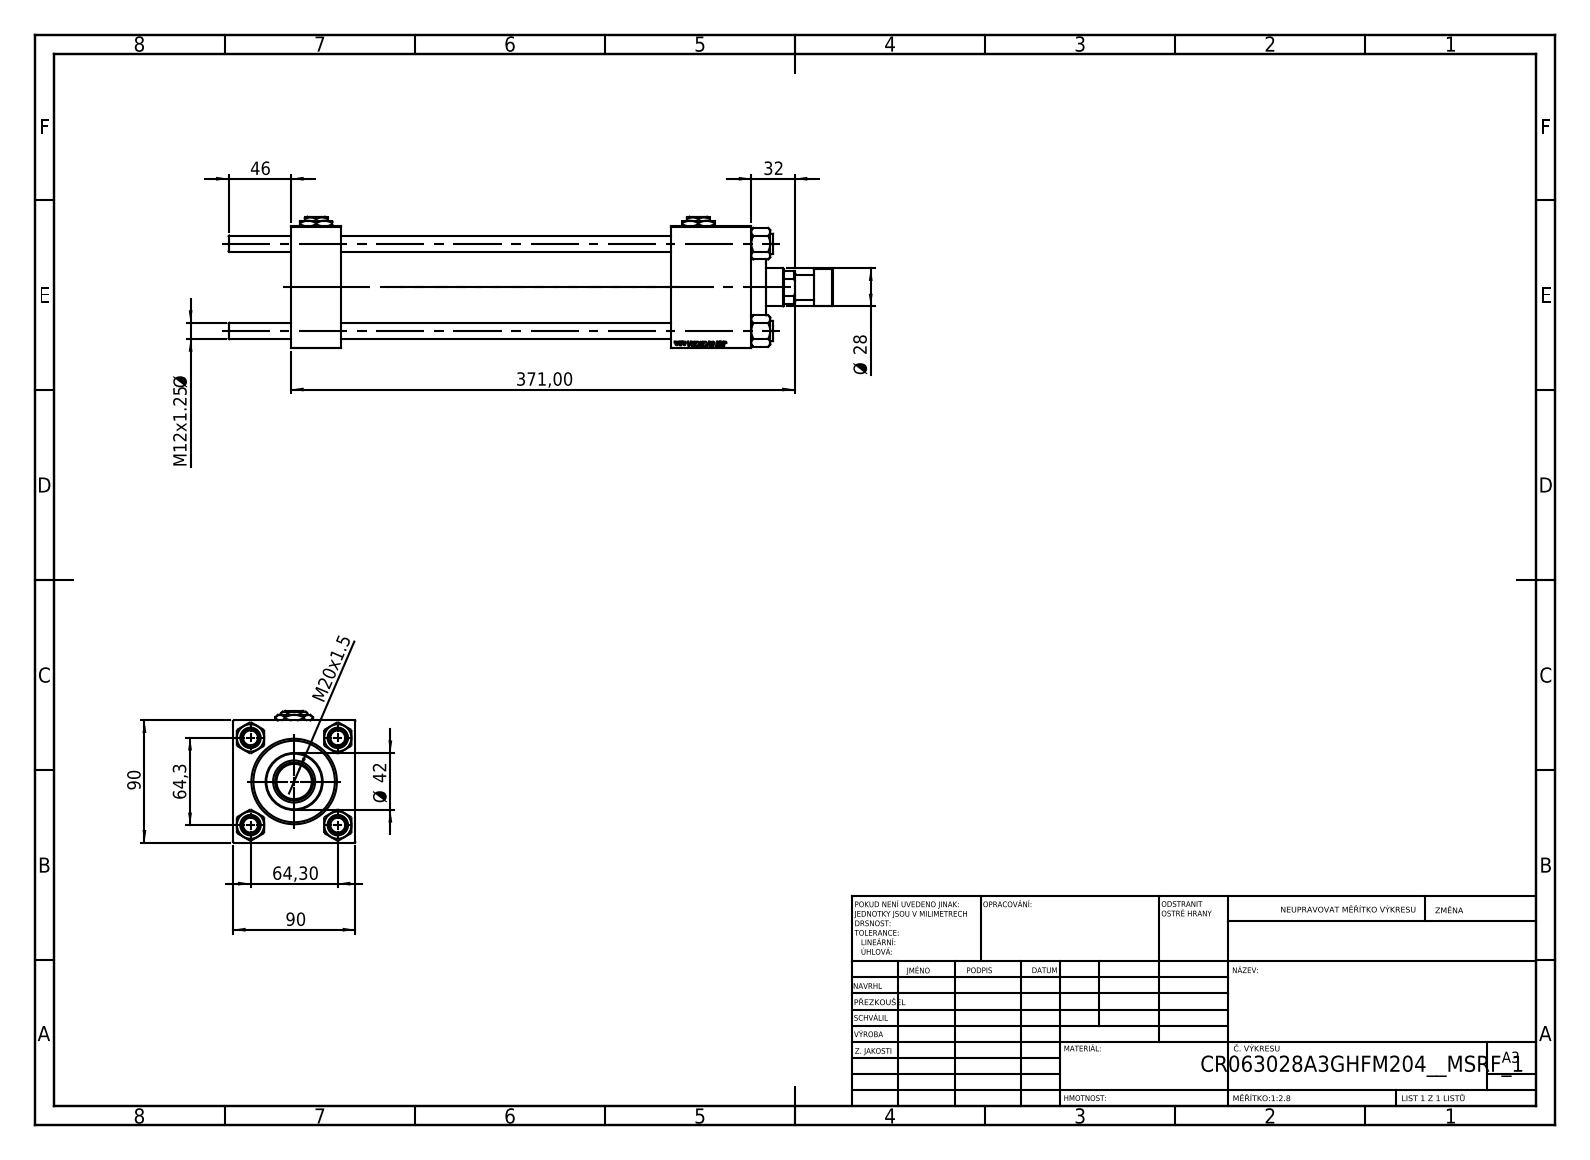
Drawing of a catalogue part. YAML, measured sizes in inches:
part_name: "V215_VC_A; CR025_012_A_0_G_A_G_M_020_+#_##_TYCINKA; NUT_M5; Zatka_pro_OIL_PORT (+3 more)"
step_written_by: "SolidWorks 2019 (CONFIG_CONTROL_DESIGN)"
units: inches
bodies: {solids: 14, faces: 1247, planar: 571, cylindrical: 92, other: 584}
overall_size: [17.52, 3.819, 3.543]
volume: 79.15
surface_area: 501.5
round_holes:
  - {diameter: 0.472, count: 4}
  - {diameter: 0.276, count: 2}
  - {diameter: 0.825, count: 2}
  - {diameter: 1.181, count: 2}
  - {diameter: 0.728, count: 1}
  - {diameter: 1.102, count: 1}
  - {diameter: 1.22, count: 1}
  - {diameter: 1.969, count: 1}
  - {diameter: 2.362, count: 1}
  - {diameter: 2.48, count: 1}
round_bosses_or_shafts:
  - {diameter: 0.591, count: 4}
  - {diameter: 2.717, count: 1}
  - {diameter: 1.654, count: 1}
  - {diameter: 1.063, count: 1}
  - {diameter: 0.709, count: 1}
face_to_face_distances: [3.543, 1.457, 13.346, 11.89, 2.323, 11.024, 9.567, 12.217, 10.76, 1.193]
hole_center_spacings: [1.79, 2.531, 3.58, 11.083]
